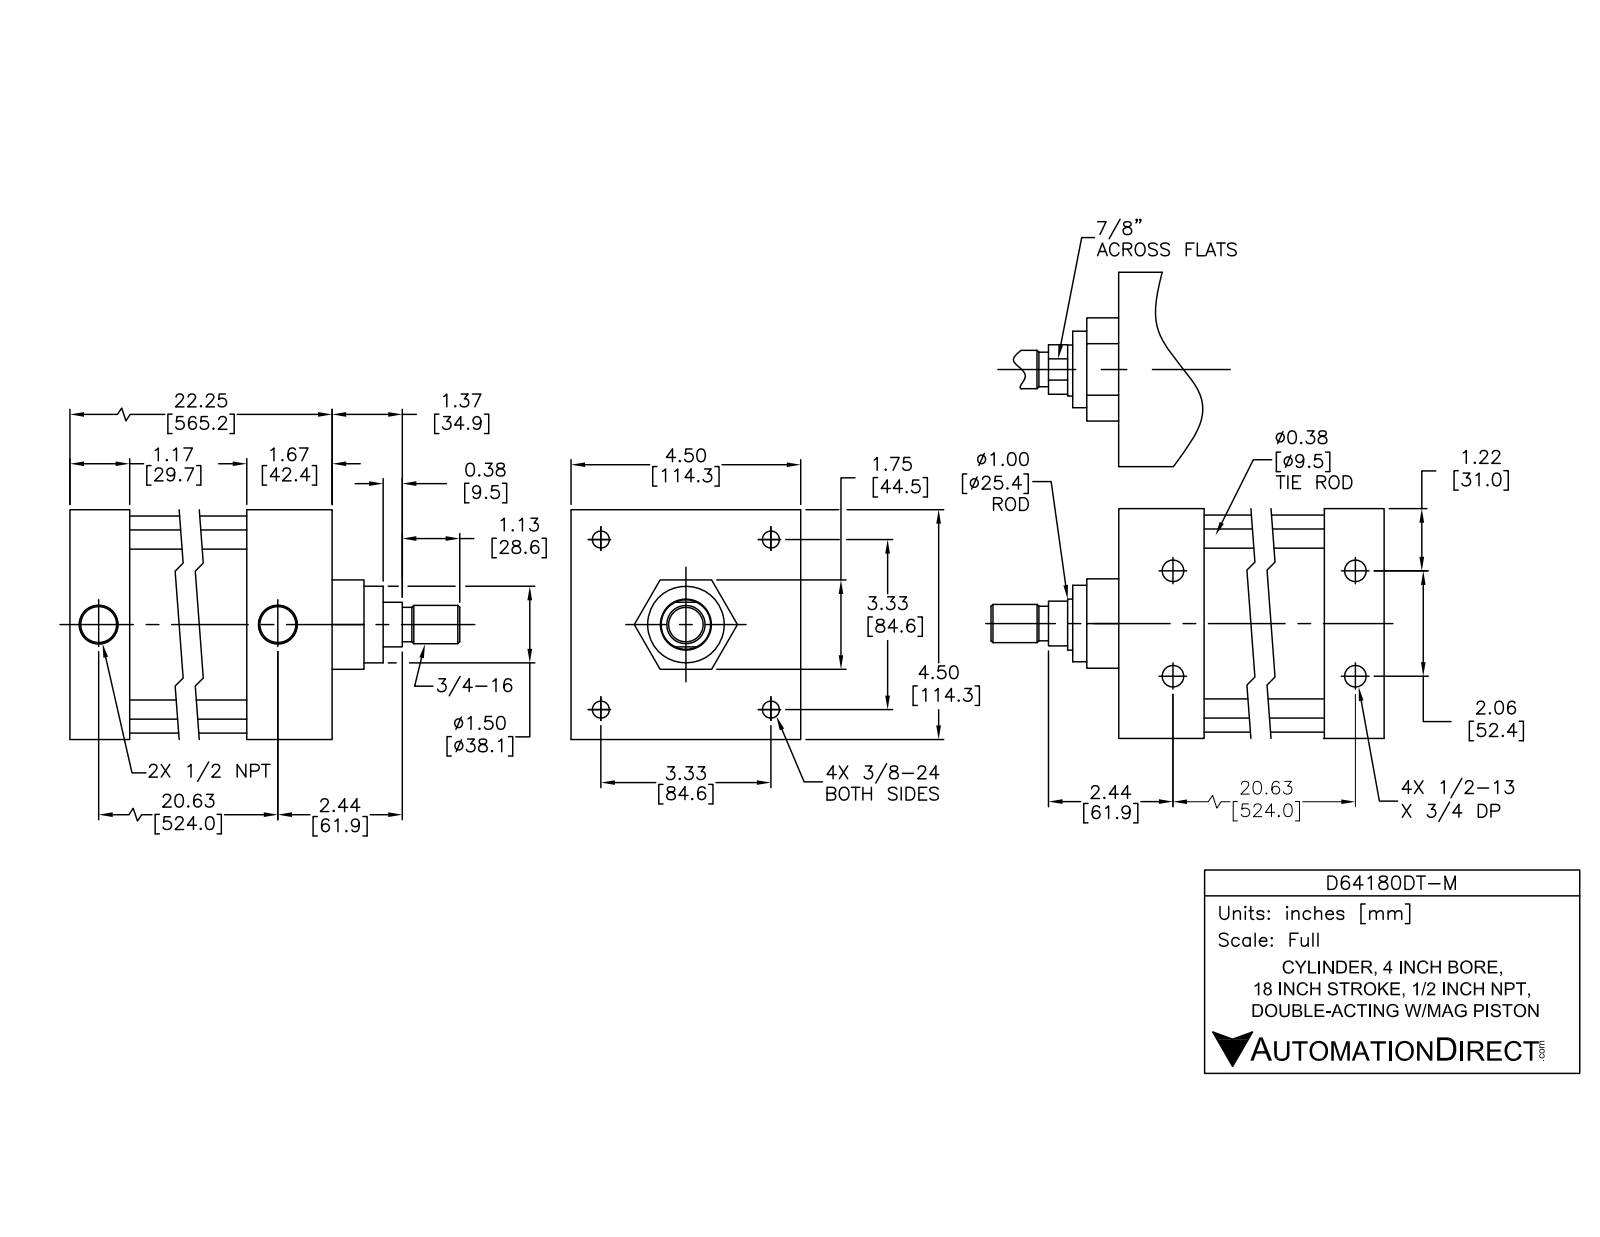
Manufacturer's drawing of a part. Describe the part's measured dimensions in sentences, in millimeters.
The part is named "D64180DT-M; D64180DT-M PISTON; D64180DT-M BODY". Its 3-D file was written by "SolidWorks 2015 (AUTOMOTIVE_DESIGN)". It is 12 solids with 303 faces: 99 planar, 114 cylindrical and 90 other. Overall it measures 628.5 by 114.3 by 114.3 millimeters. Its volume is 2 083 000 cubic millimeters and its surface area 574 300 square millimeters. Round holes: 4 of diameter 8.4, 4 of diameter 10.3, 4 of diameter 10.6, 4 of diameter 15.9, 2 of diameter 12.7, 2 of diameter 19.5, 1 of diameter 25.4, 1 of diameter 25.5, 1 of diameter 101.6. Round bosses or shafts: 4 of diameter 15.5, 4 of diameter 9.5, 4 of diameter 8.6, 1 of diameter 108, 1 of diameter 101.5, 1 of diameter 44.5, 1 of diameter 25.3, 1 of diameter 24.6. Partial cylindrical surfaces (rounded edges, fillets, slot ends): 4 of radius 11.4. The main face-to-face distances are 114.3, 2, 490.9, 565, 44.5, 533.3, 31.7, 501.7, 31.6, 63.4. The hole center spacings are 26.2, 59.7, 84.4, 524.5, 523.8, 52.4, 119.3, 526.4.
